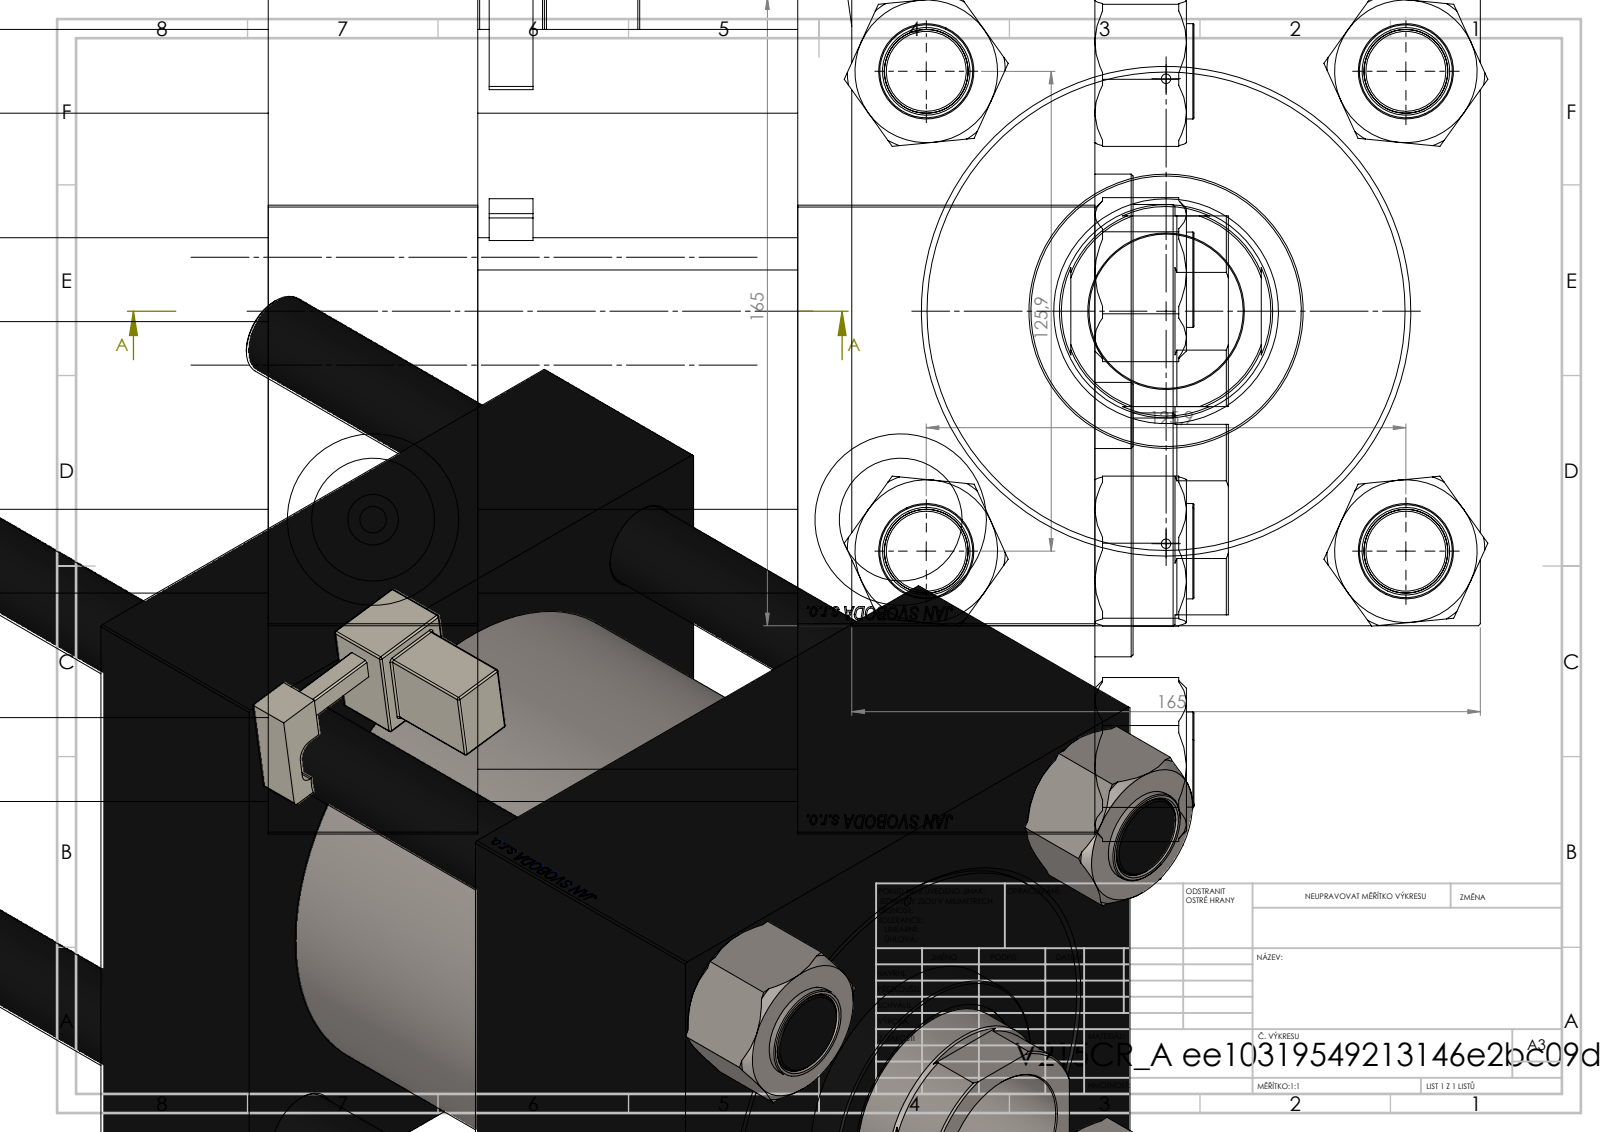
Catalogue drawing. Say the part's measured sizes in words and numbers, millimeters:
The part is named "CR025_012_A_0_G_A_G_M_020_+#_##_TYCINKA; V215CR_BODY_A; V215CR_VCP; V215_VC_A (+2 more)". Its 3-D file was written by "SolidWorks 2019 (CONFIG_CONTROL_DESIGN)". It is 12 solids with 1265 faces: 599 planar, 112 cylindrical and 554 other. Overall it measures 333 by 178.03 by 168.94 millimeters. Its volume is 4 701 000 cubic millimeters and its surface area 555 090 square millimeters. Round holes: 4 of diameter 22, 2 of diameter 2.5, 2 of diameter 7, 2 of diameter 32.24, 2 of diameter 45, 1 of diameter 40.5, 1 of diameter 56, 1 of diameter 59, 1 of diameter 96, 1 of diameter 125, 1 of diameter 125.5. Round bosses or shafts: 4 of diameter 25, 1 of diameter 131, 1 of diameter 72, 1 of diameter 6. Partial cylindrical surfaces (rounded edges, fillets, slot ends): 24 of radius 0.5, 1 of radius 1, 1 of radius 2.5, 1 of radius 4, 1 of radius 27. The main face-to-face distances are 165, 55, 162, 217, 139, 84, 78, 188.3, 133.3, 49.3. The hole center spacings are 62.98, 89.02, 125.9, 139.02, 61, 178.05, 122, 138.5.
